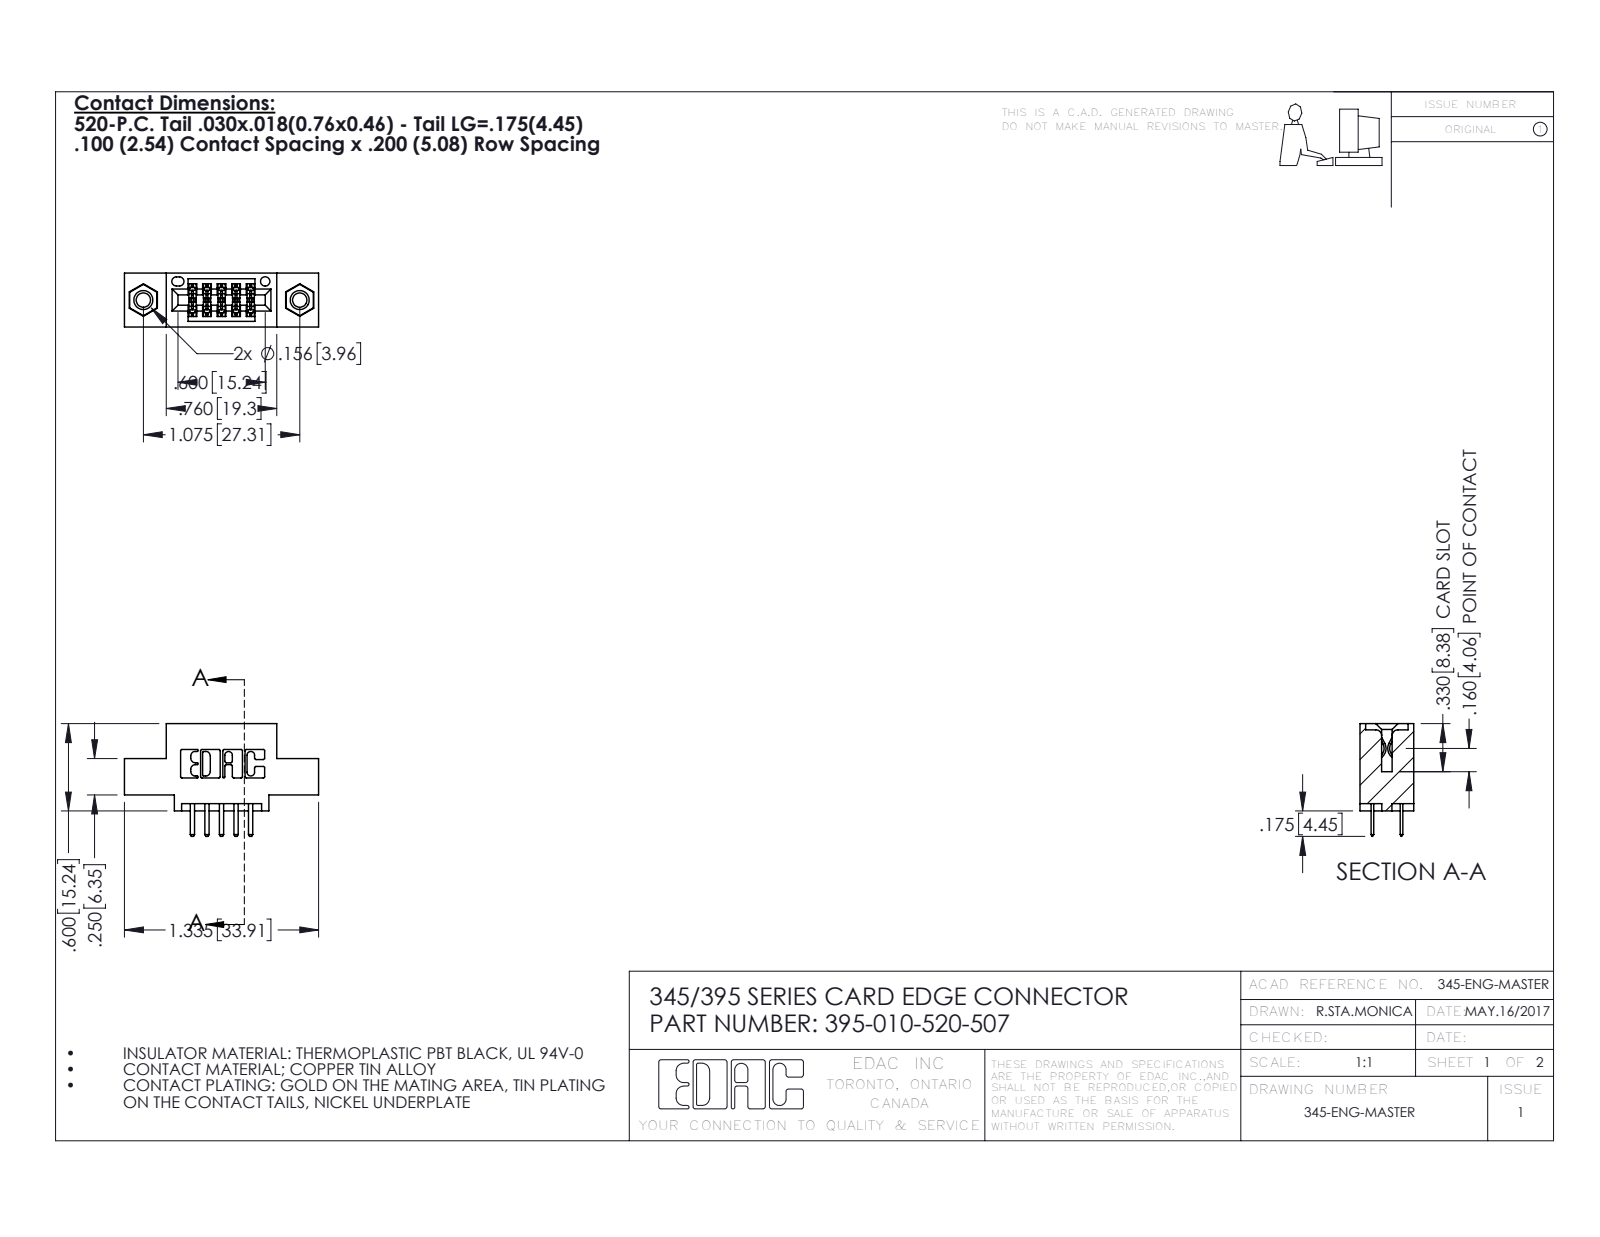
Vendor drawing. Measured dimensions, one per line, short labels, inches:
name: 345-292-001_345-293-120; 345-250-001_345-250-005-103; 345 Part_0.110 Offset - 0.156 Dia-TI; 395-010-520-507
written by: SolidWorks 2016 (CONFIG_CONTROL_DESIGN)
unit: in
bodies: 13 solids, 730 faces (466 planar, 248 cylindrical, 16 other)
size: 1.335 × 0.775 × 0.37
volume: 0.174 in³; area: 5.613 in²
holes: 2× ⌀0.098, 2× ⌀0.125, 2× ⌀0.156, 1× ⌀0.064
bosses: 2× ⌀0.155
rounds: 22× R0.01, 15× R0.006, 14× R0.01, 6× R0.007, 6× R0.031, 3× R0.026, 2× R0.014, 2× R0.019
face distances: 0.2, 0.37, 0.072, 0.298, 0.1, 0.25, 0.025, 0.098, 0.272, 0.06
hole spacings: 0.27, 0.847, 1.075
